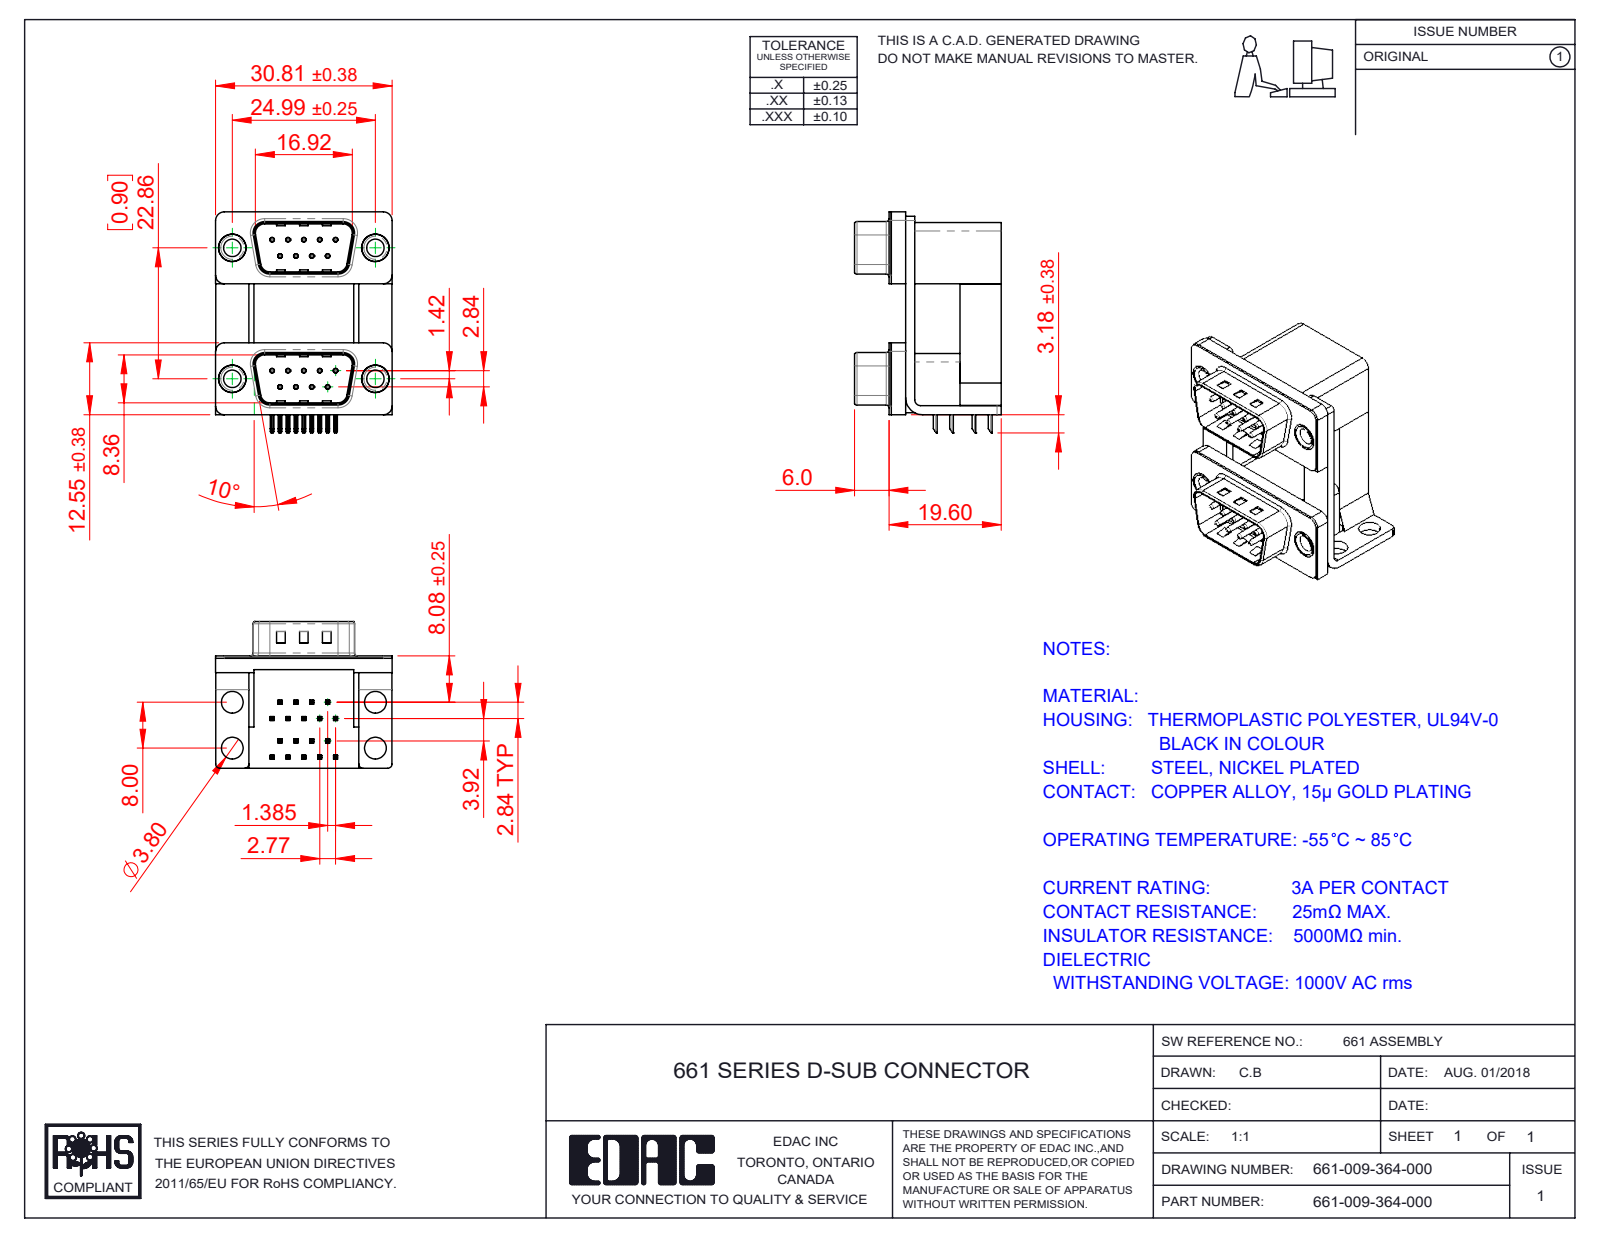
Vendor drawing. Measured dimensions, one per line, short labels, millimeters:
name: 661 Contact Bottom Upper_H; 661-009-364-000; 661 Housing Upper_09 Contacts H; 661 Contact Top Upper_H (+7 more)
written by: SolidWorks 2020 (CONFIG_CONTROL_DESIGN)
unit: mm
bodies: 29 solids, 1864 faces (1152 planar, 558 cylindrical, 154 other)
size: 38.59 × 30.81 × 25.6
volume: 10 783 mm³; area: 12 237 mm²
holes: 18× ⌀0.35, 18× ⌀0.8, 4× ⌀3.05, 4× ⌀3.5, 4× ⌀3.8, 4× ⌀4, 4× ⌀4.8, 4× ⌀5
bosses: 18× ⌀0.75, 4× ⌀4.9, 4× ⌀4.75, 4× ⌀3.85
rounds: 72× R0.25, 36× R0.12, 16× R0.5, 14× R1.5, 8× R0.75, 8× R0.9, 8× R1.6, 8× R2
face distances: 0.4, 2.5, 22.86, 12, 16.7, 19.2, 7.2, 9.5, 12.4, 1.6
hole spacings: 3.16, 2.77, 23.03, 22.86, 5.54, 23.52, 20.07, 25.74
